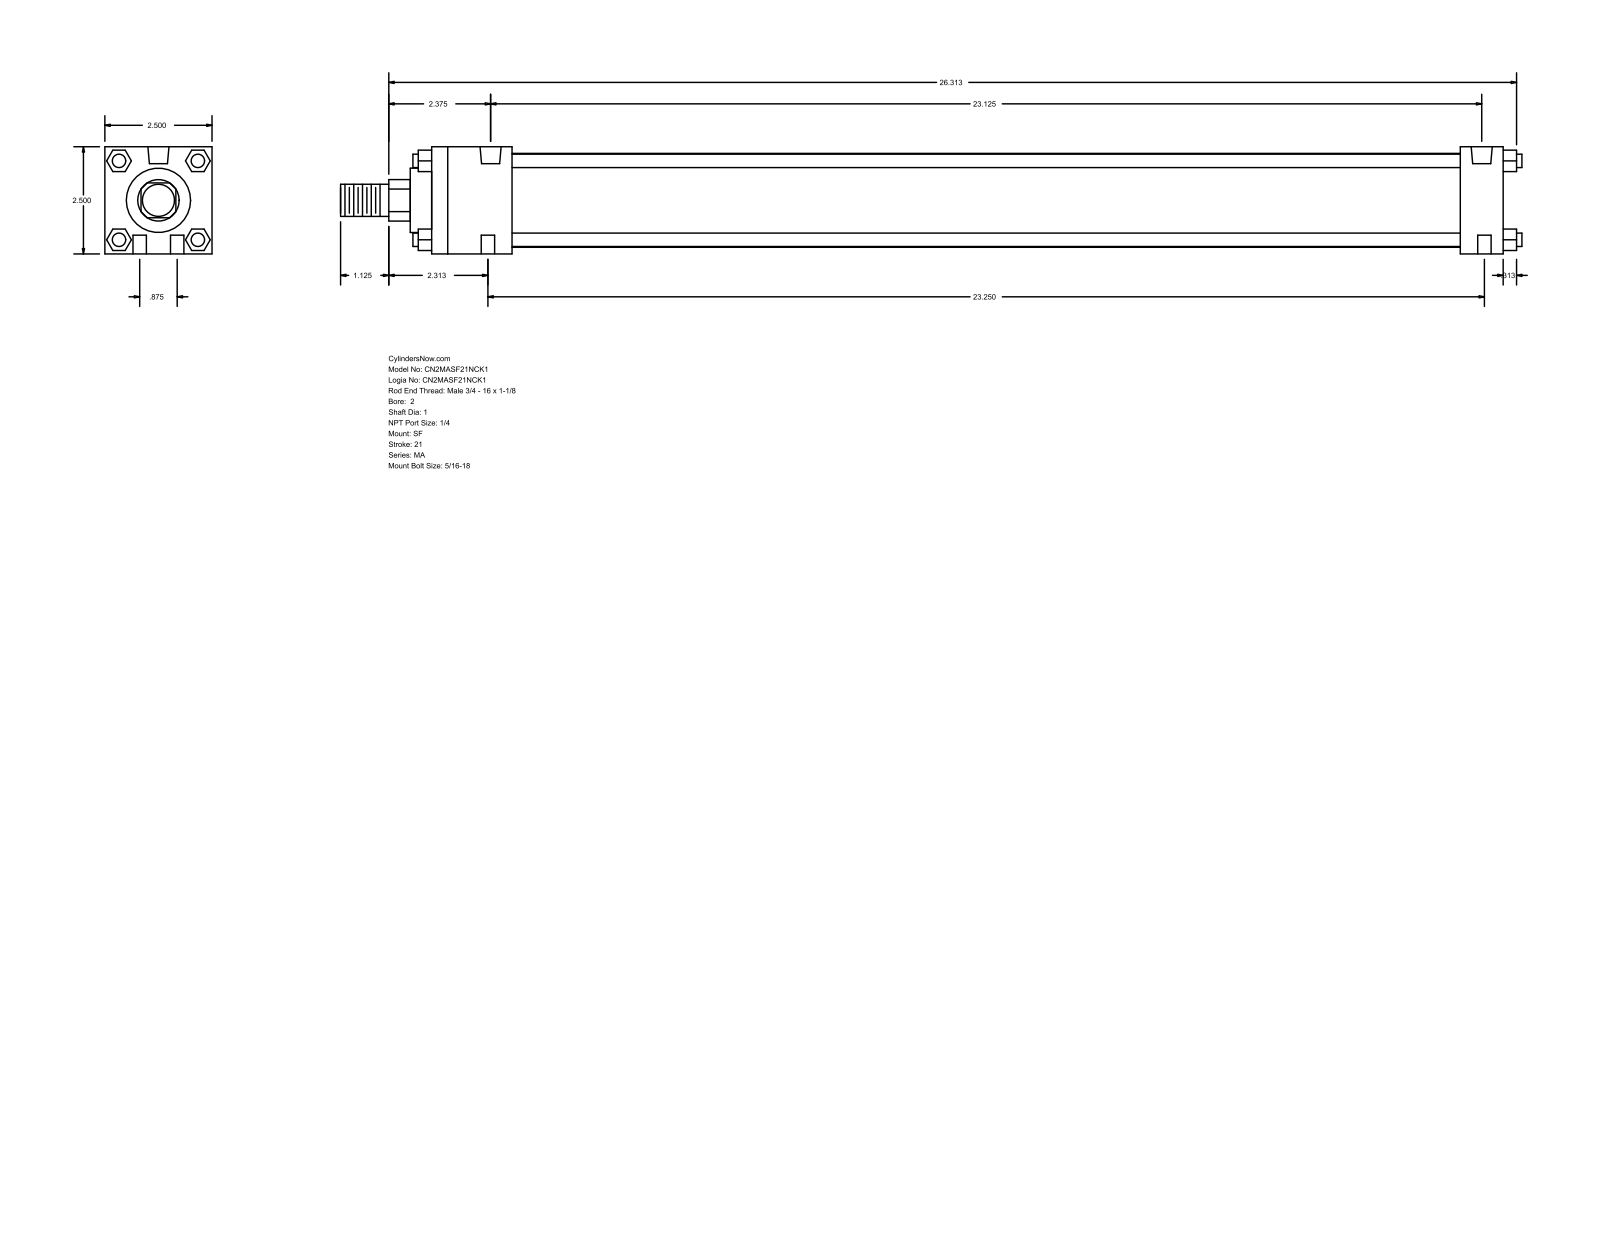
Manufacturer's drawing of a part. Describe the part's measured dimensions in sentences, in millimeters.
The part is named "MA_SF__0200_1". Its 3-D file was written by "GSSL Pune (CONFIG_CONTROL_DESIGN)". It is 0 solids with 124 faces: 94 planar, 30 cylindrical and 0 other. Overall it measures 700.09 by 63.5 by 63.5 millimeters. Round holes: 6 of diameter 7.94, 2 of diameter 12.49. Round bosses or shafts: 4 of diameter 7.94, 1 of diameter 55.63, 1 of diameter 38.1, 1 of diameter 25.4, 1 of diameter 19.05. Partial cylindrical surfaces (rounded edges, fillets, slot ends): 1 of radius 12.29. The main face-to-face distances are 63.5, 635, 12.7, 25.4, 609.6, 47.63, 561.97, 587.37, 23.37, 40.47. The hole center spacings are 11.22, 589.06, 22.22, 587.37, 590.55, 590.97.
